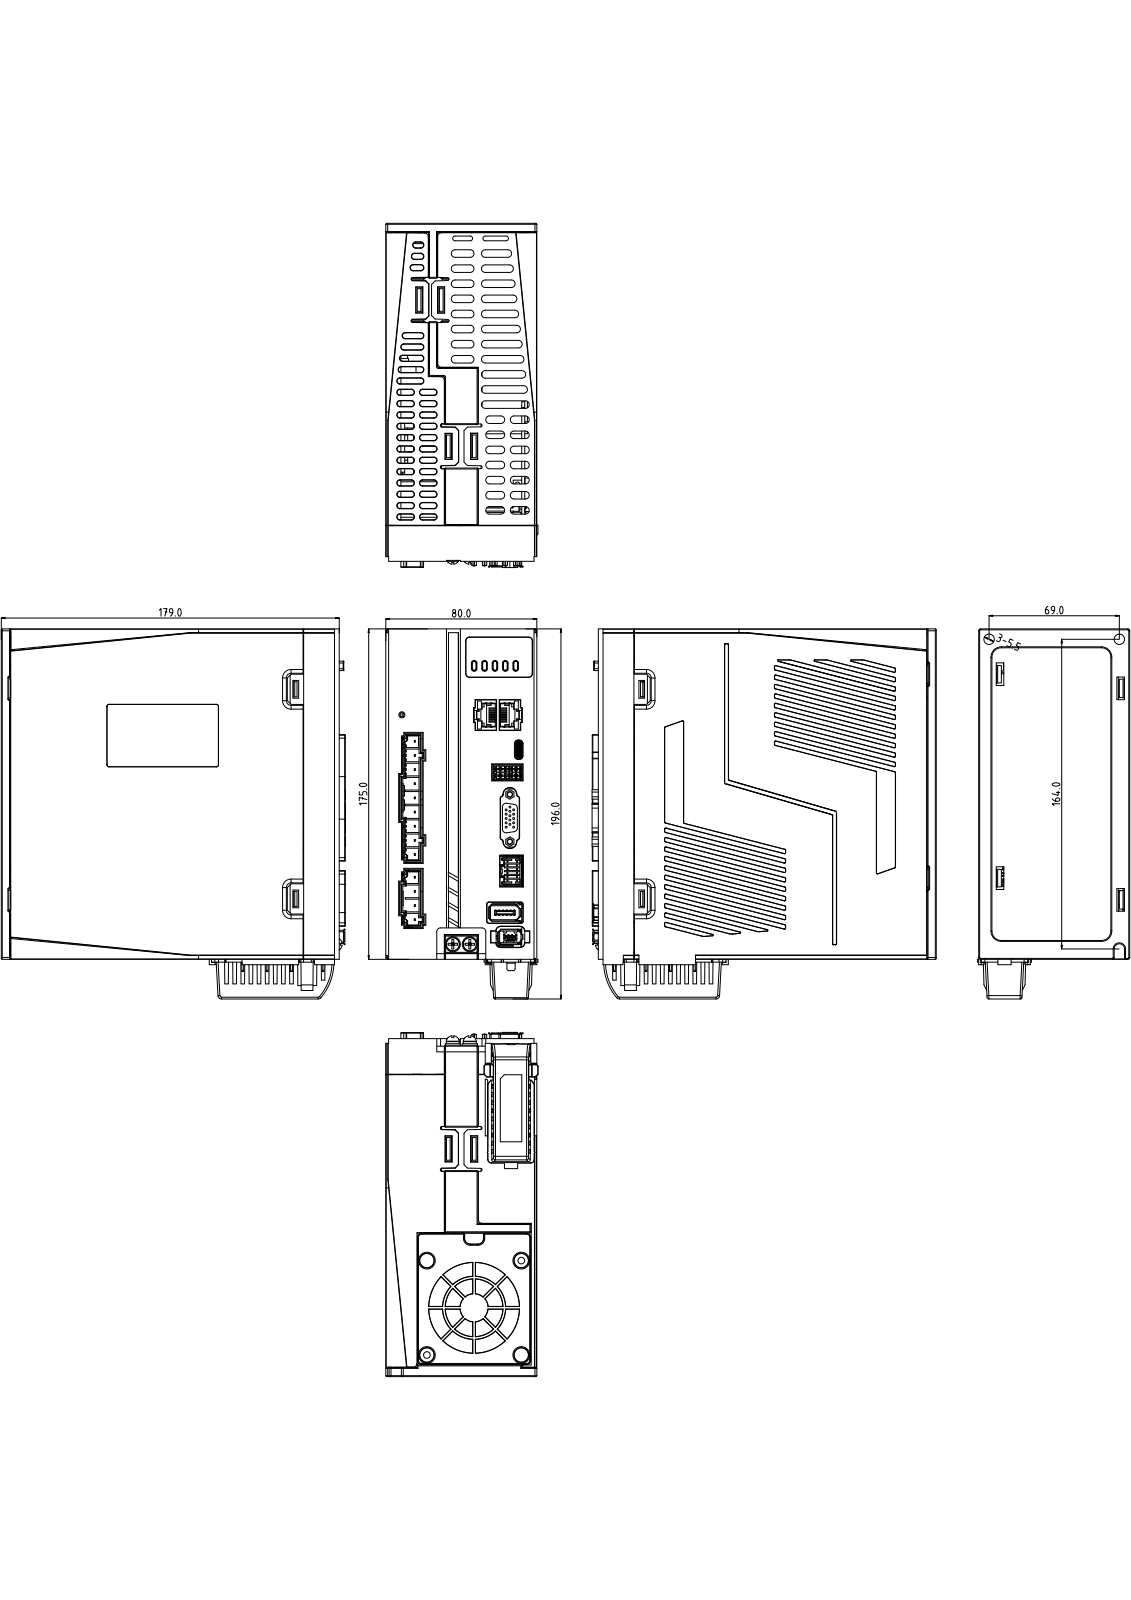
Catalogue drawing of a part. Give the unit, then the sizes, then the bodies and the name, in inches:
Units: inches
Overall size (bounding box): 7.717 × 7.177 × 3.173
Round holes (diameter × count): ⌀0.087 ×16, ⌀0.039 ×15, ⌀0.098 ×8, ⌀0.138 ×6, ⌀0.049 ×4, ⌀0.126 ×4, ⌀0.022 ×3, ⌀0.11 ×2, ⌀0.147 ×2, ⌀0.157 ×2, ⌀0.177 ×2, ⌀0.217 ×2
Round bosses / shafts (diameter × count): ⌀0.165 ×15, ⌀0.236 ×6, ⌀0.256 ×5, ⌀0.098 ×4, ⌀0.197 ×3, ⌀1.398 ×2, ⌀0.315 ×2, ⌀0.268 ×2
Partial cylindrical surfaces — rounded edges, fillets, slot ends (radius × count): R0.02 ×342, R0.012 ×174, R0.079 ×99, R0.008 ×84, R0.039 ×69, R0.004 ×52, R0.006 ×43, R0.016 ×40
Main face-to-face distances: 0.079, 0.236, 2.835, 3.071, 2.756, 0.315, 0.157, 2.598, 0.063, 2.898
Hole centre spacings: 0.09, 0.18, 0.18, 0.238, 0.27, 0.097, 0.098, 0.156
Volume: 40.66 in³ · Surface area: 730.9 in²
Bodies: 34 solids, 8498 faces (5854 planar, 1680 cylindrical, 964 other)
Part name (STEP PRODUCT): M4X10_GB818_1_1_1_1_1; D4_GB9074_26_1_1_1_1_1; D4_GB9074_24_1_1_1_1_1; M4X10_GB9074_4_ASM_1_ASM_1_ASM__ASM (+8 more)
STEP written by: PRO/ENGINEER BY PARAMETRIC TECHNOLOGY CORPORATION, 2010280 (CONFIG_CONTROL_DESIGN)
